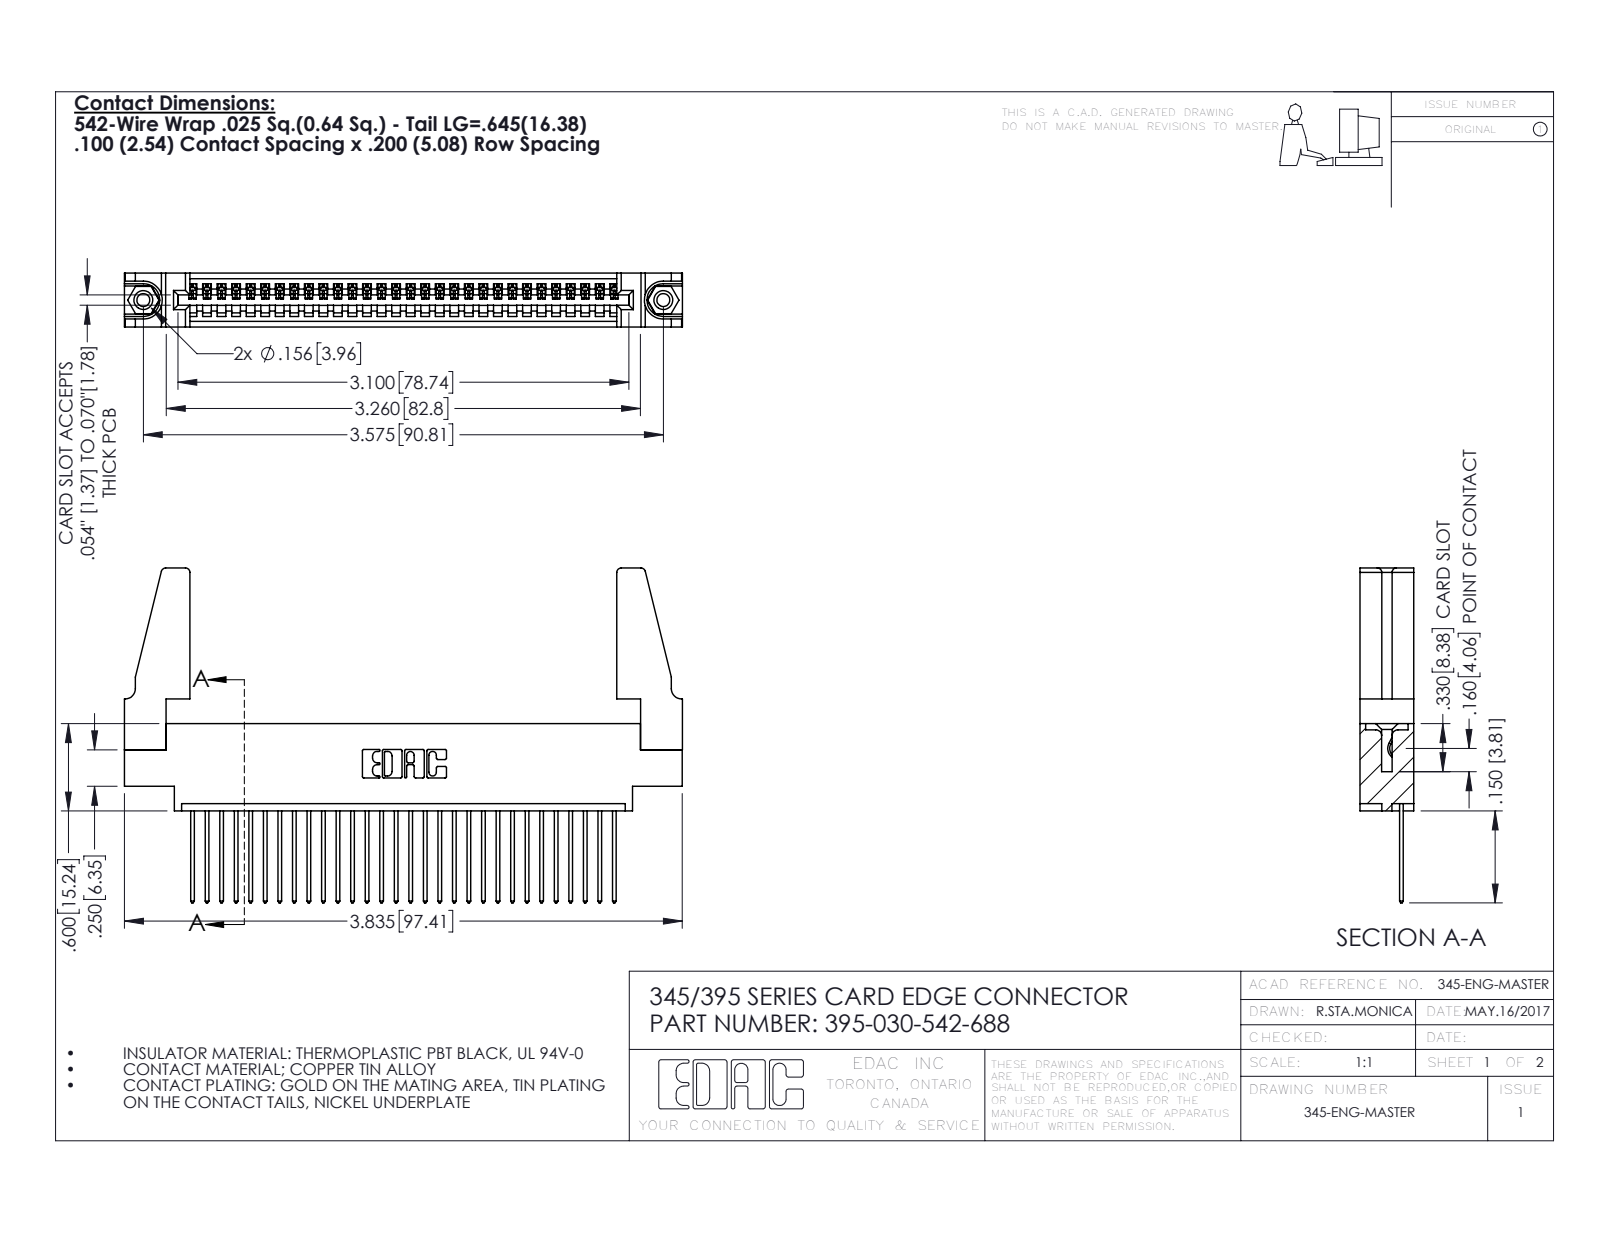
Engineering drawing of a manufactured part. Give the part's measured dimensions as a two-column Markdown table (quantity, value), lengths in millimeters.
| quantity | value |
| --- | --- |
| part name | 345-220-078_345-220-088; 345 Part_0.170 Offset - 0.156 Dia-TH; 345-250-001_345-250-001-102; 395-030-542-688 (+1 more) |
| STEP written by | SolidWorks 2016 (CONFIG_CONTROL_DESIGN) |
| units | millimeters |
| bodies | 35 solids, 1994 faces (1356 planar, 622 cylindrical, 16 other) |
| overall size | 97.4 × 58.5 × 9.4 |
| volume | 12 400 mm³ |
| surface area | 15 620 mm² |
| round holes (diameter × count) | 2.3 × 2, 3.2 × 2, 4 × 2, 1.6 × 1 |
| round bosses / shafts (diameter × count) | 3.9 × 2 |
| partial cylindrical surfaces (radius × count) | 0.2 × 60, 0.3 × 60, 0.3 × 22, 0.8 × 8, 0.2 × 6, 0.8 × 6, 0.7 × 3, 0.8 × 2 |
| main face-to-face distances | 1.8, 9.4, 7.6, 2.5, 6.9, 0.6, 5.1, 5.7, 4.4, 3.8 |
| hole center spacings | 6.9, 84.8, 90.8 |
